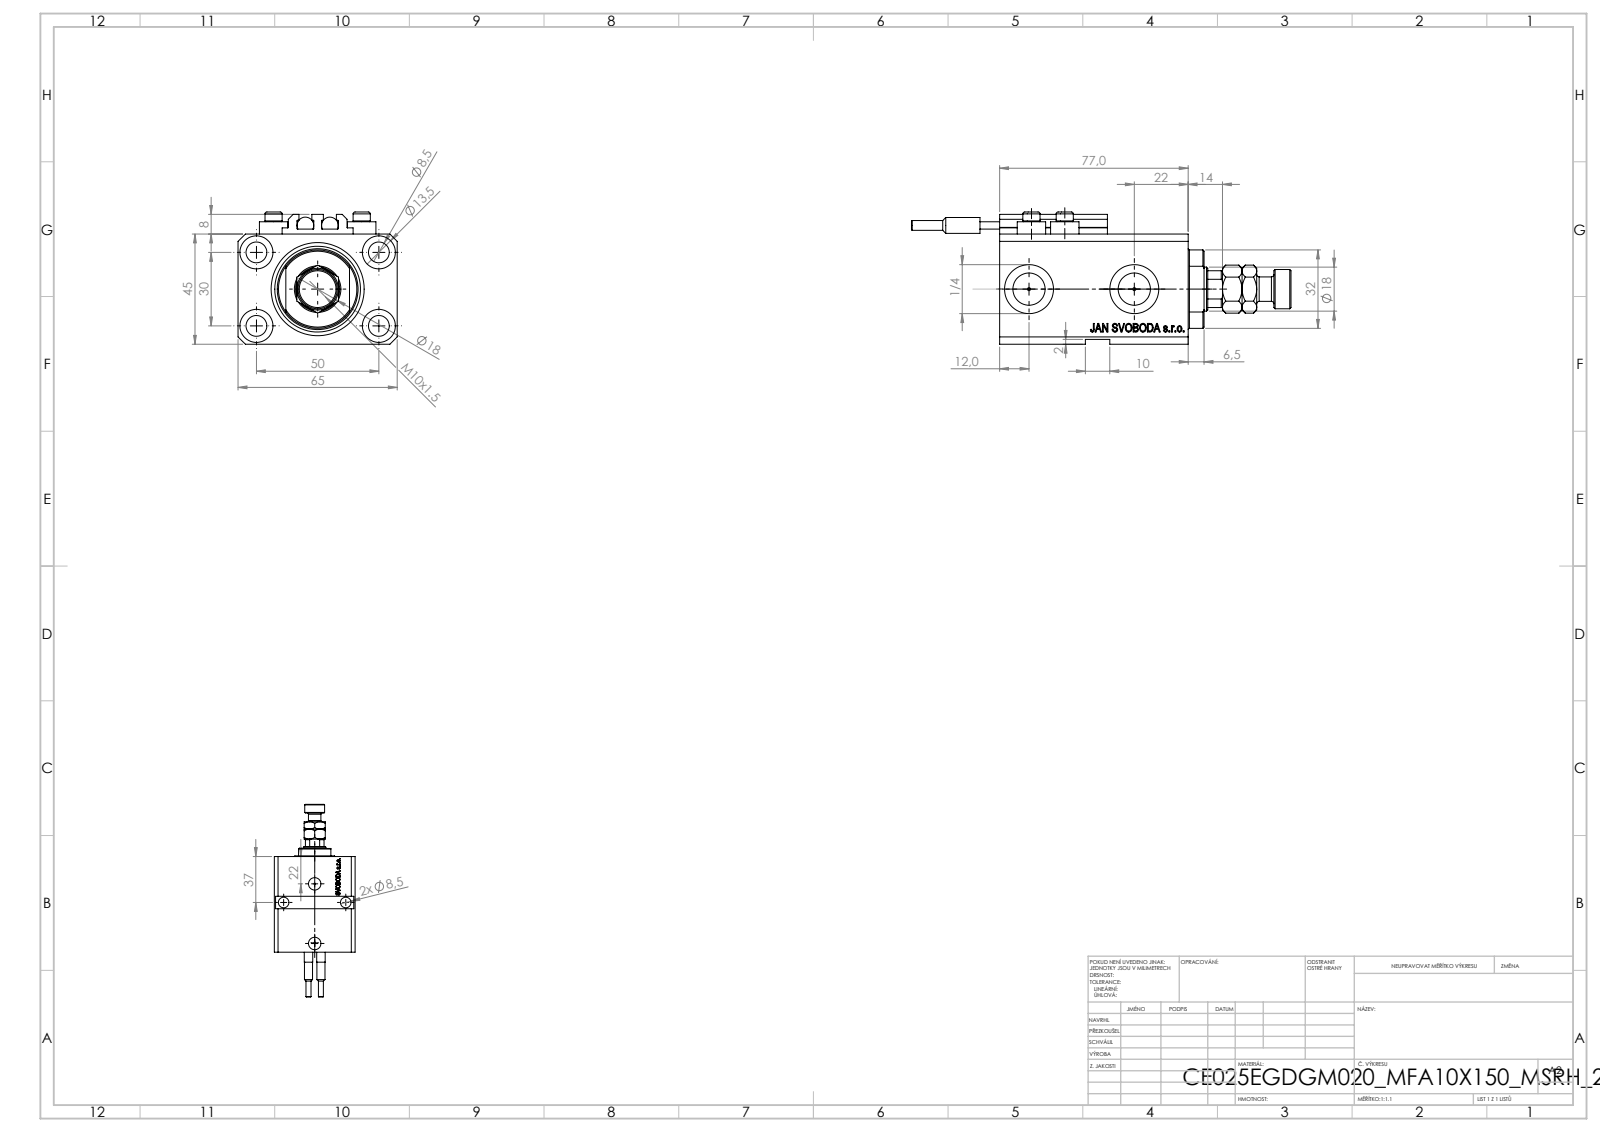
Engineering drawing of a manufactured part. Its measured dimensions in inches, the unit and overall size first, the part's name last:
Units: inches
Overall size (bounding box): 6.102 × 2.559 × 2.126
Round holes (diameter × count): ⌀0.335 ×7, ⌀0.049 ×4, ⌀0.157 ×4, ⌀0.531 ×4, ⌀0.394 ×2, ⌀0.518 ×2, ⌀0.787 ×2, ⌀0.709 ×1, ⌀0.984 ×1, ⌀1.496 ×1
Round bosses / shafts (diameter × count): ⌀0.457 ×4, ⌀0.276 ×4, ⌀0.268 ×2, ⌀0.256 ×2, ⌀0.157 ×2, ⌀0.63 ×1, ⌀0.394 ×1
Partial cylindrical surfaces — rounded edges, fillets, slot ends (radius × count): R0.008 ×10, R0.335 ×1, R0.63 ×1
Main face-to-face distances: 1.772, 2.559, 0.551, 2.48, 0.079, 3.031, 0.118, 0.272, 1.85, 0.197
Hole centre spacings: 1.148, 1.969, 0.535, 0.595, 0.741, 0.747, 1.032, 1.048
Volume: 12.52 in³ · Surface area: 101 in²
Bodies: 11 solids, 1187 faces (563 planar, 154 cylindrical, 470 other)
Part name (STEP PRODUCT): V250CE_VC_E; SWITCH_V250CE; ALLEN BOLT V250CE; MFA (+2 more)
STEP written by: SolidWorks 2019 (CONFIG_CONTROL_DESIGN)
